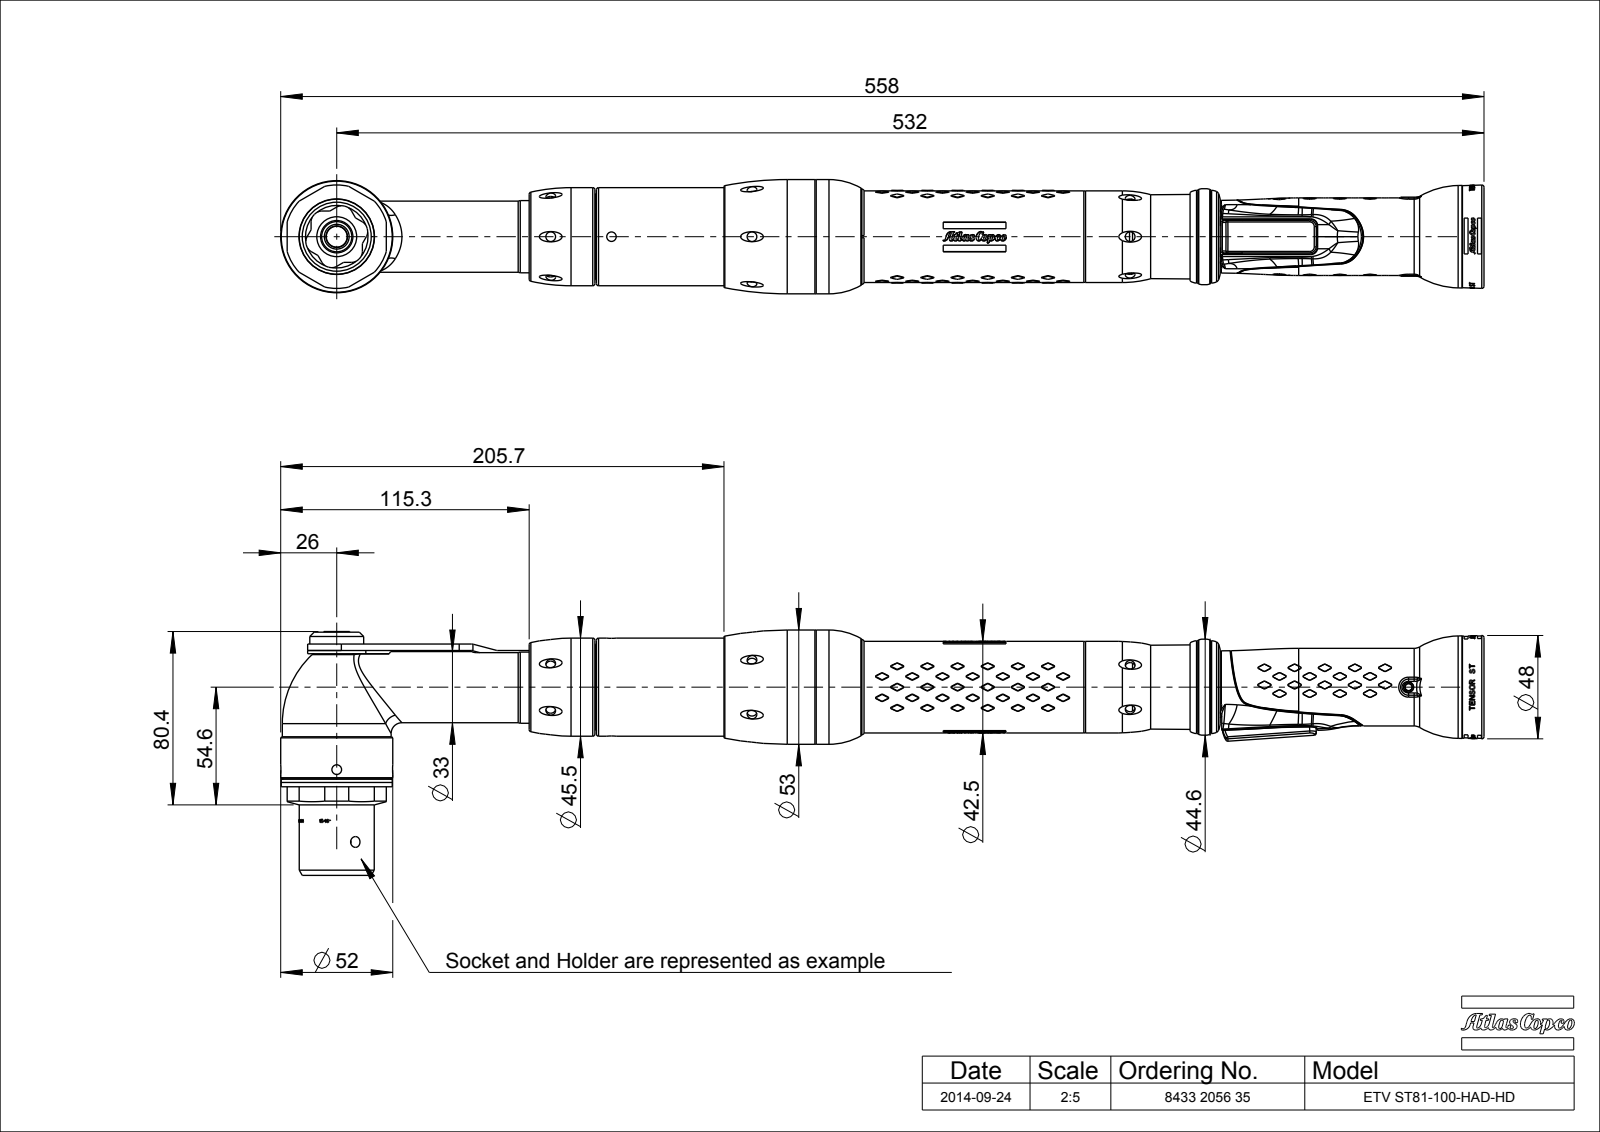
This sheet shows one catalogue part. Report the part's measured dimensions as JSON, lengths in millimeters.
{"part_name": "4220232200; 4220241310; 4220241380_ASM; 4220230300 (+8 more)", "step_written_by": "PRO/ENGINEER BY PARAMETRIC TECHNOLOGY CORPORATION, 2013410 (CONFIG_CONTROL_DESIGN)", "units": "millimeters", "bodies": {"solids": 34, "faces": 4386, "planar": 1645, "cylindrical": 800, "other": 1941}, "overall_size": [558.4, 113.8, 53], "volume_mm3": 281956, "surface_area_mm2": 243140, "round_holes": [[2.64, 12], [3.27, 12], [3.6, 11], [4.5, 11], [2.6, 4], [45.6, 2], [2.2, 1], [2.5, 1], [3.2, 1], [4.4, 1], [4.7, 1], [5, 1]], "round_bosses_or_shafts": [[2.55, 5], [2.2, 5], [1.9, 5], [1.57, 5], [3.2, 4], [53, 1], [52, 1], [51.5, 1]], "partial_cylinders_radius": [[2, 16], [0.5, 13], [4.5, 12], [1.5, 10], [3, 10], [1, 9], [0.3, 8], [0.45, 8]], "face_to_face_distances": [3, 1.5, 15.5, 23, 59.5, 62.5, 4.5, 23.2, 17, 58], "hole_center_spacings": [4.48, 15, 21.21, 4.4, 5.56, 7.67, 7.75, 8.82]}
